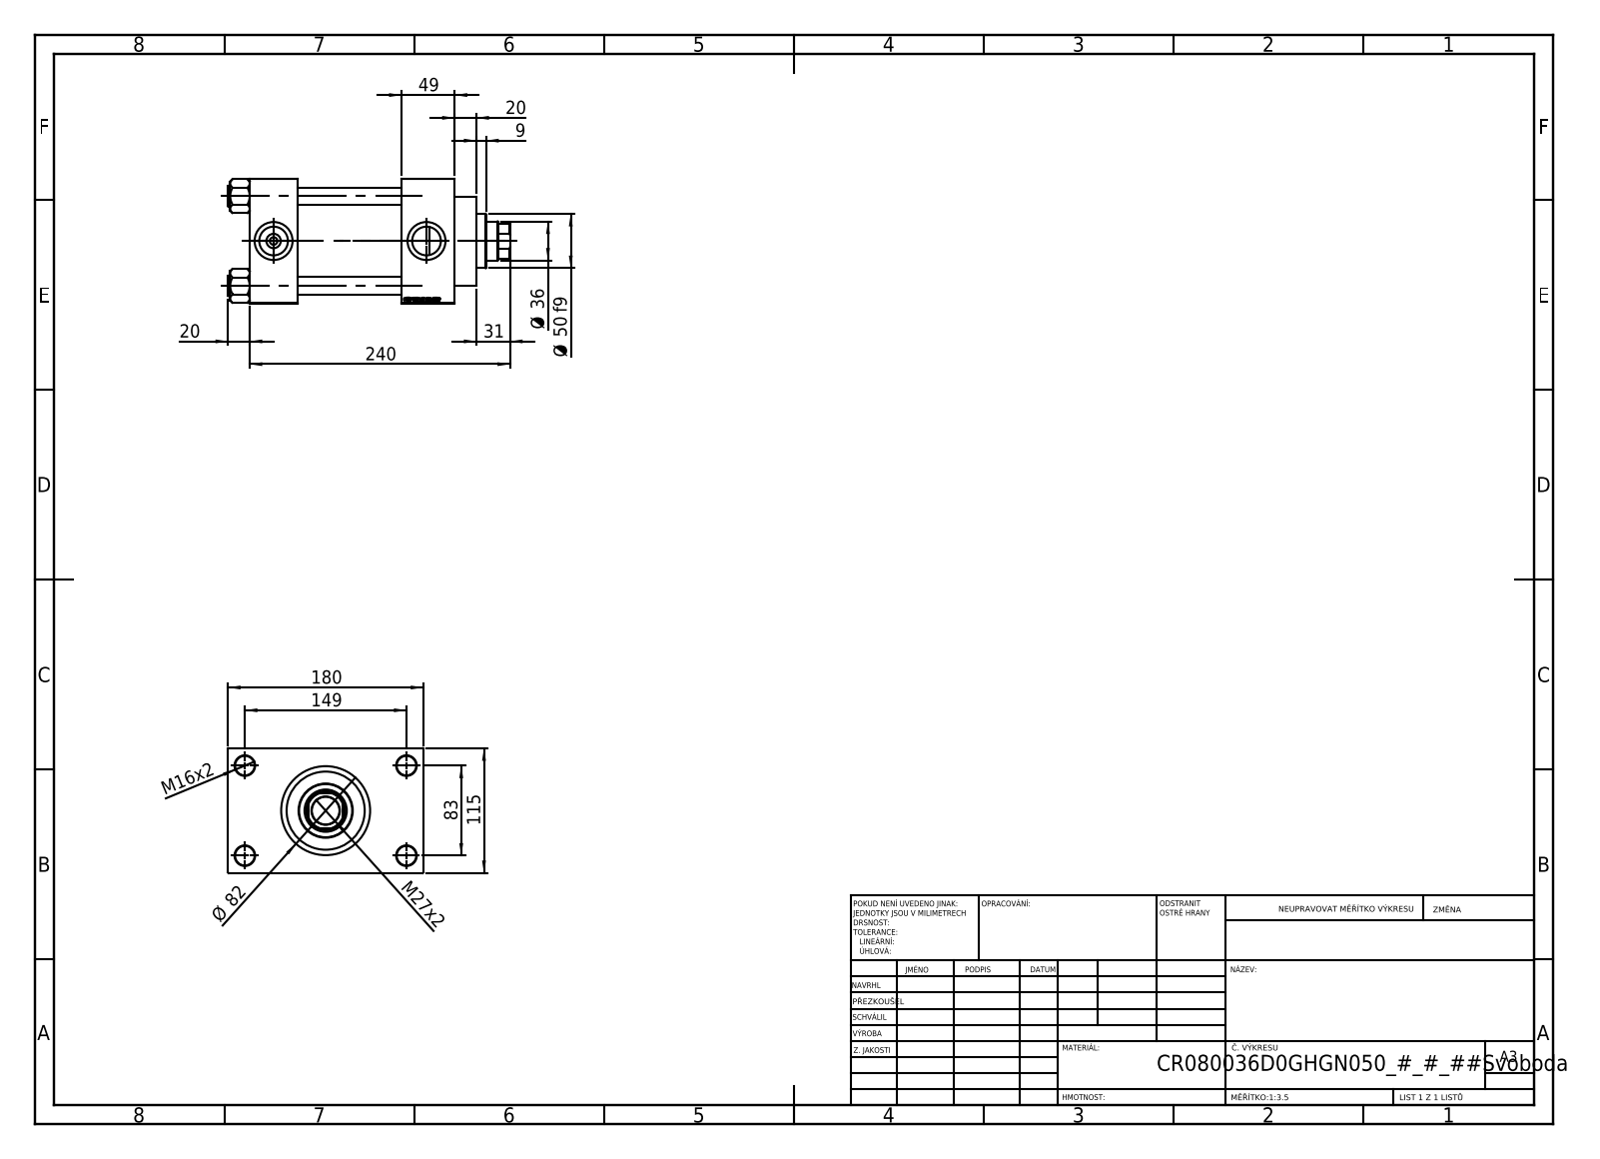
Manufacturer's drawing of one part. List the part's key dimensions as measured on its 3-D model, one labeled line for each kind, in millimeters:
Part name (STEP PRODUCT): V215CR_VCP_D; V215_VC_A; NUT_M5_D; V215CR_D_TYCINKA (+1 more)
STEP written by: SolidWorks 2019 (CONFIG_CONTROL_DESIGN)
Units: millimetres
Bodies: 11 solids, 1151 faces (545 planar, 88 cylindrical, 518 other)
Overall size (bounding box): 260 × 180 × 115
Volume: 2 058 000 mm³ · Surface area: 321 664 mm²
Round holes (diameter × count): ⌀16 ×4, ⌀18 ×4, ⌀7 ×2, ⌀26.44 ×2, ⌀35 ×2, ⌀25.5 ×1, ⌀36 ×1, ⌀39 ×1, ⌀61 ×1, ⌀72 ×1, ⌀80 ×1
Round bosses / shafts (diameter × count): ⌀19 ×4, ⌀86 ×1, ⌀82 ×1, ⌀50 ×1
Partial cylindrical surfaces — rounded edges, fillets, slot ends (radius × count): R17.5 ×1
Main face-to-face distances: 115, 96, 145, 49, 44, 140, 189, 32.5, 147.5, 180
Hole centre spacings: 33.15, 58.48, 82.7, 85.28, 89.24, 115.85, 142.43, 83
